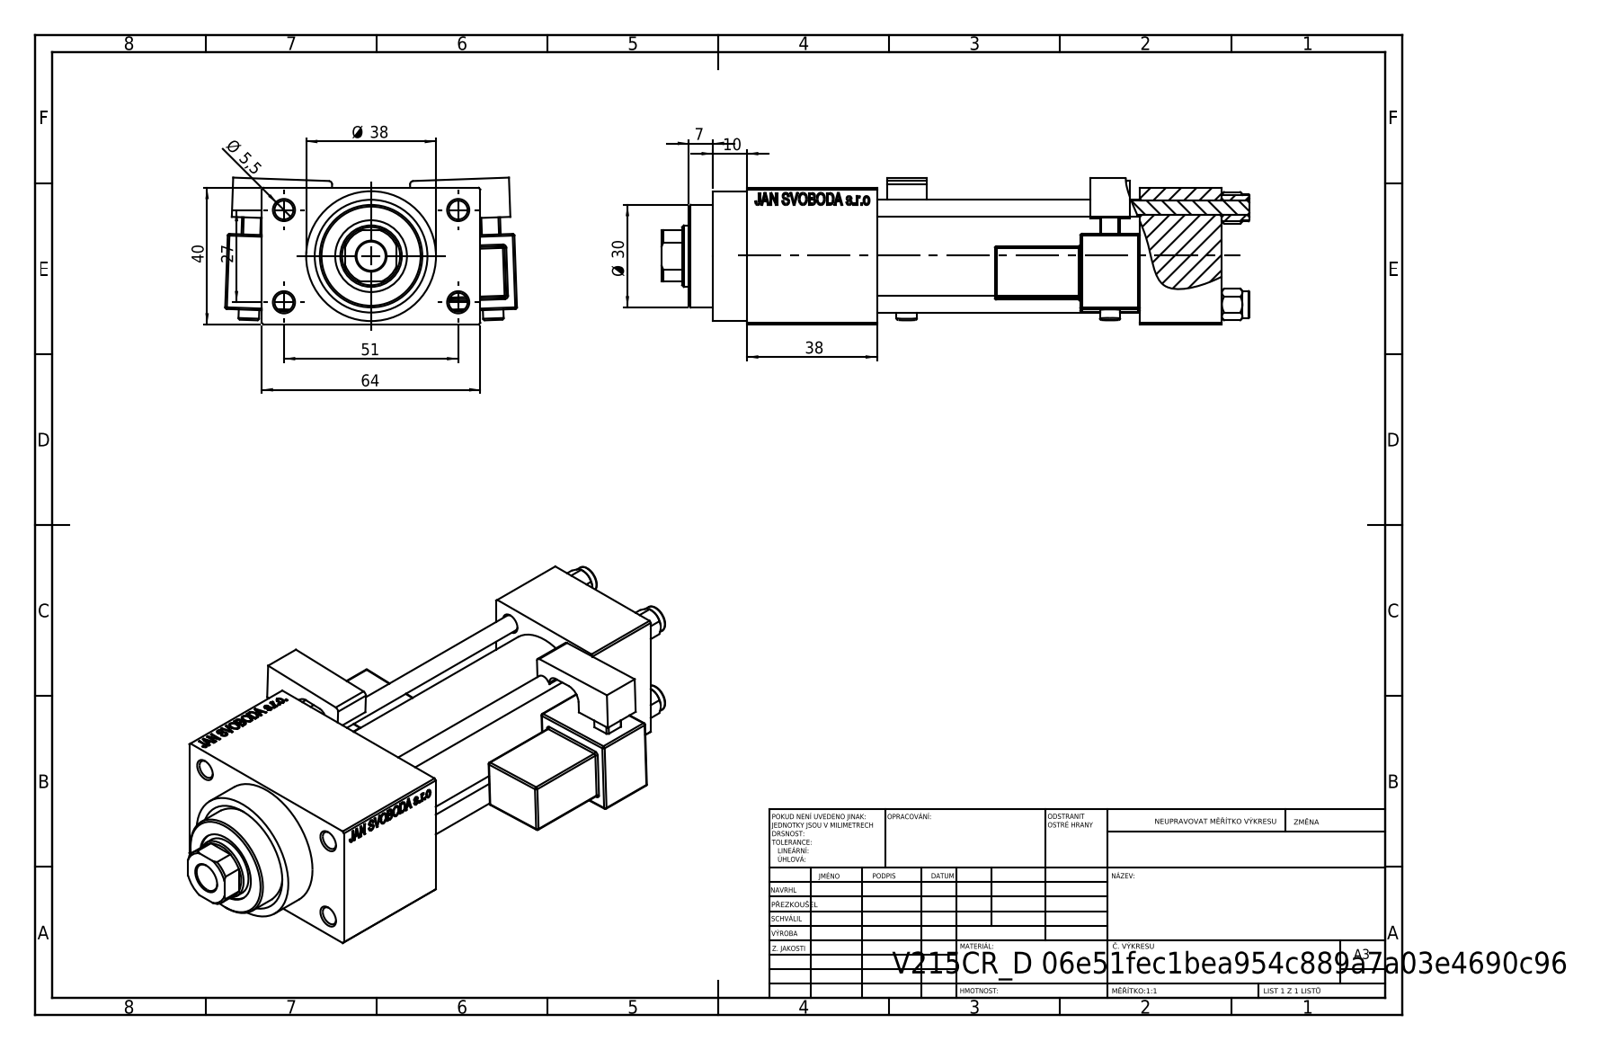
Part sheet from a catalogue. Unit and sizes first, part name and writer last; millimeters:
Units: millimetres
Overall size (bounding box): 172 × 85.39 × 42.99
Round holes (diameter × count): ⌀5 ×4, ⌀5.5 ×4, ⌀20 ×3, ⌀7 ×2, ⌀13.16 ×2, ⌀8.5 ×1, ⌀18 ×1, ⌀21 ×1, ⌀25 ×1, ⌀30 ×1
Round bosses / shafts (diameter × count): ⌀8 ×4, ⌀6 ×2, ⌀38 ×1, ⌀31 ×1
Partial cylindrical surfaces — rounded edges, fillets, slot ends (radius × count): R0.5 ×48, R1 ×2, R2.5 ×2, R4 ×2, R8.5 ×1
Main face-to-face distances: 40, 77, 12, 20, 24, 3, 101, 52, 38, 139
Hole centre spacings: 11.37, 20.01, 28.3, 28.85, 29.89, 39.66, 48.34, 27
Volume: 237 596 mm³ · Surface area: 85 447 mm²
Bodies: 13 solids, 1259 faces (557 planar, 146 cylindrical, 556 other)
Part name (STEP PRODUCT): V215CR_MSU; V215CR_D_TYCINKA; V215CR_D_Body; V215CR_VCP_D (+2 more)
STEP written by: SolidWorks 2019 (CONFIG_CONTROL_DESIGN)
